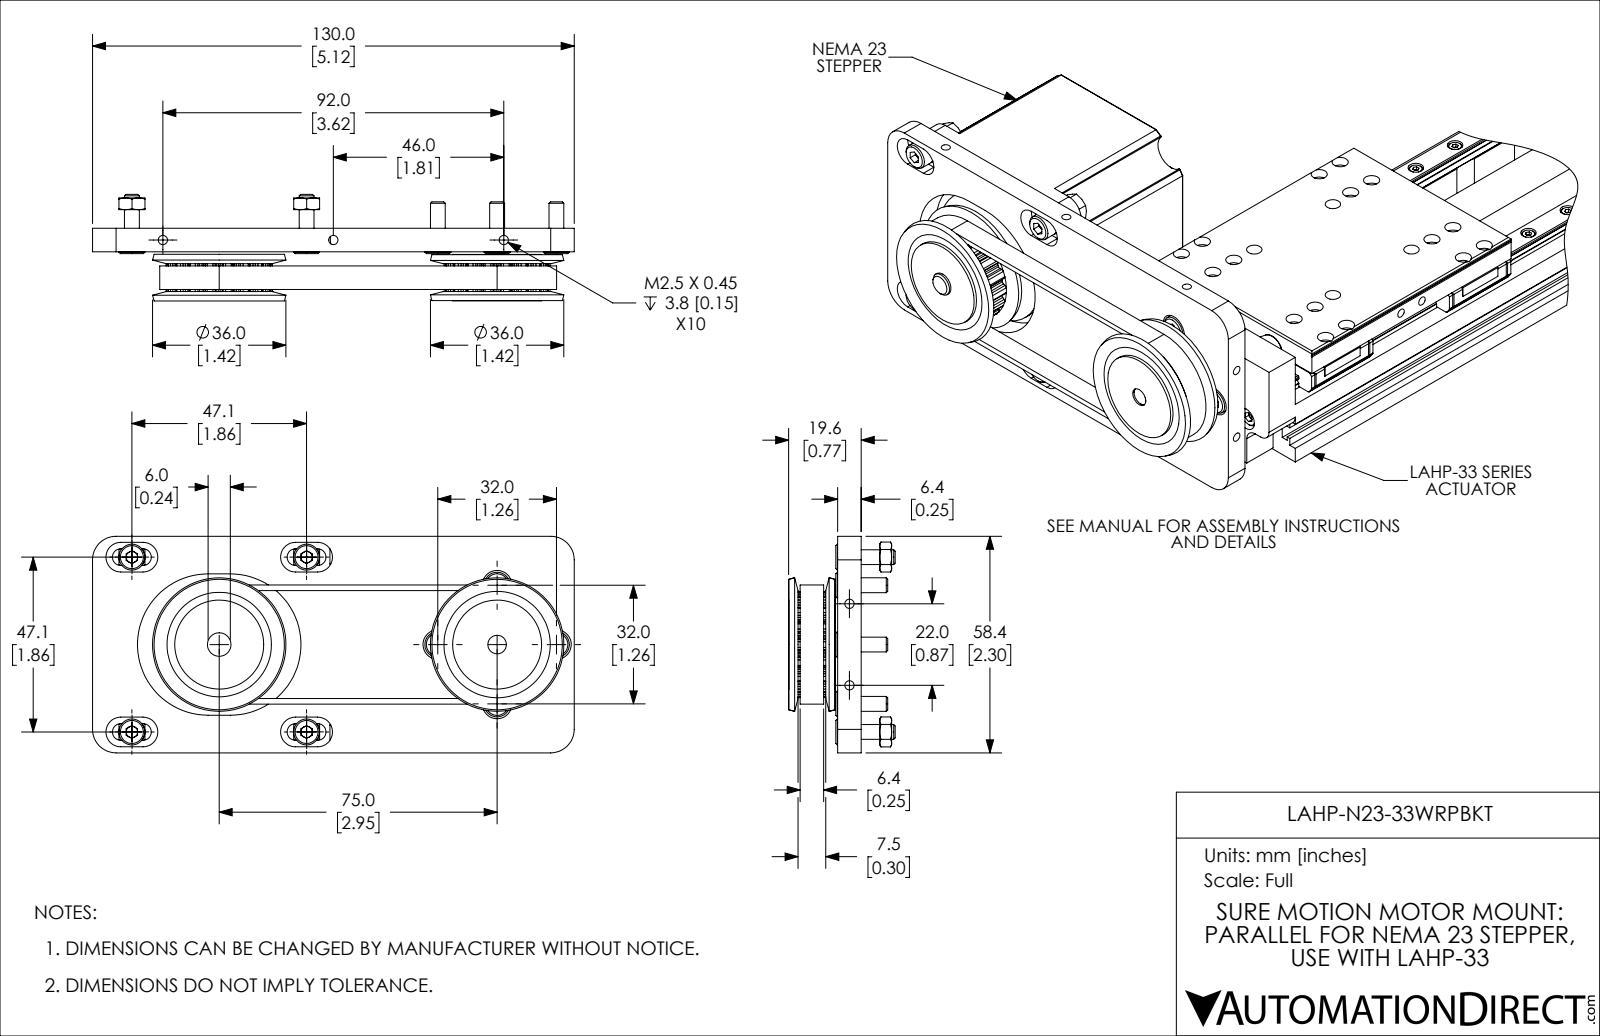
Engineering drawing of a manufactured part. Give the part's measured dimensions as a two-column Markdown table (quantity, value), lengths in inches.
| quantity | value |
| --- | --- |
| part name | LAHP-N23-33WRPBKT |
| STEP written by | SolidWorks 2019 (CONFIG_CONTROL_DESIGN) |
| units | inches |
| bodies | 26 solids, 975 faces (376 planar, 415 cylindrical, 184 other) |
| overall size | 5.118 × 2.3 × 1.132 |
| volume | 3.34 in³ |
| surface area | 51.87 in² |
| round holes (diameter × count) | 0.169 × 8, 0.098 × 5, 0.128 × 4, 0.13 × 4, 0.157 × 4, 0.177 × 4, 0.315 × 4, 0.197 × 1, 0.25 × 1, 0.867 × 1 |
| round bosses / shafts (diameter × count) | 0.157 × 10, 0.276 × 8, 0.945 × 2 |
| partial cylindrical surfaces (radius × count) | 0.024 × 144, 0.089 × 8, 0.157 × 8, 0.25 × 4, 0.508 × 2, 0.563 × 2, 0.573 × 2, 0.632 × 2 |
| main face-to-face distances | 0.25, 0.577, 1.723, 0.77, 0.52, 0.278, 0.028, 0.492, 0.399, 0.035 |
| hole center spacings | 0.63, 0.891, 1.312, 1.855, 1.856, 1.856, 1.857, 2.625 |
